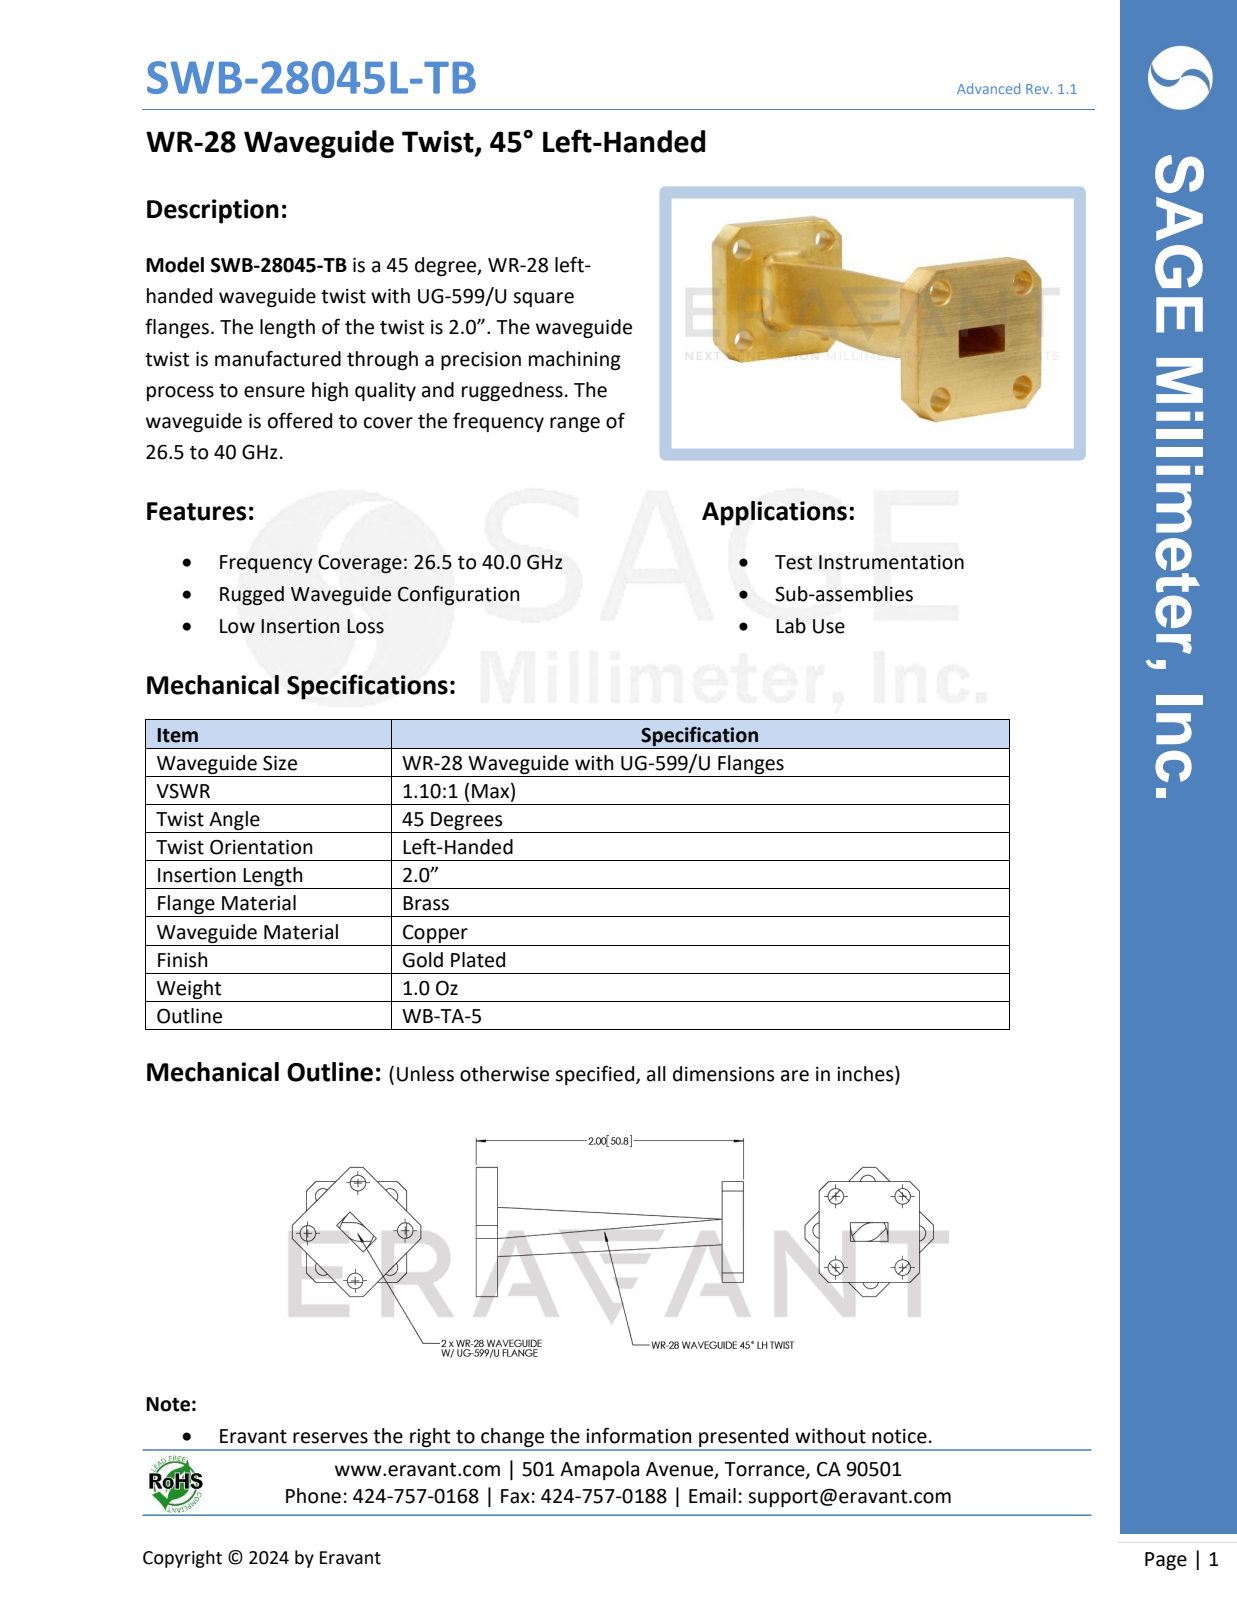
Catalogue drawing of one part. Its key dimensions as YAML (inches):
part_name: "SWB-28045L-TB"
step_written_by: "SolidWorks 2016 (CONFIG_CONTROL_DESIGN)"
units: inches
bodies: {solids: 2, faces: 51, planar: 31, cylindrical: 16, other: 4}
overall_size: [2, 0.962, 0.962]
volume: 0.258
surface_area: 5.093
round_holes:
  - {diameter: 0.116, count: 8}
face_to_face_distances: [0.16, 2, 1.84, 1.84, 1.68, 0.16, 0.75, 0.75, 0.856, 0.106]
hole_center_spacings: [0.279, 0.5, 0.53, 0.673, 0.729, 0.259, 0.298, 0.665]
